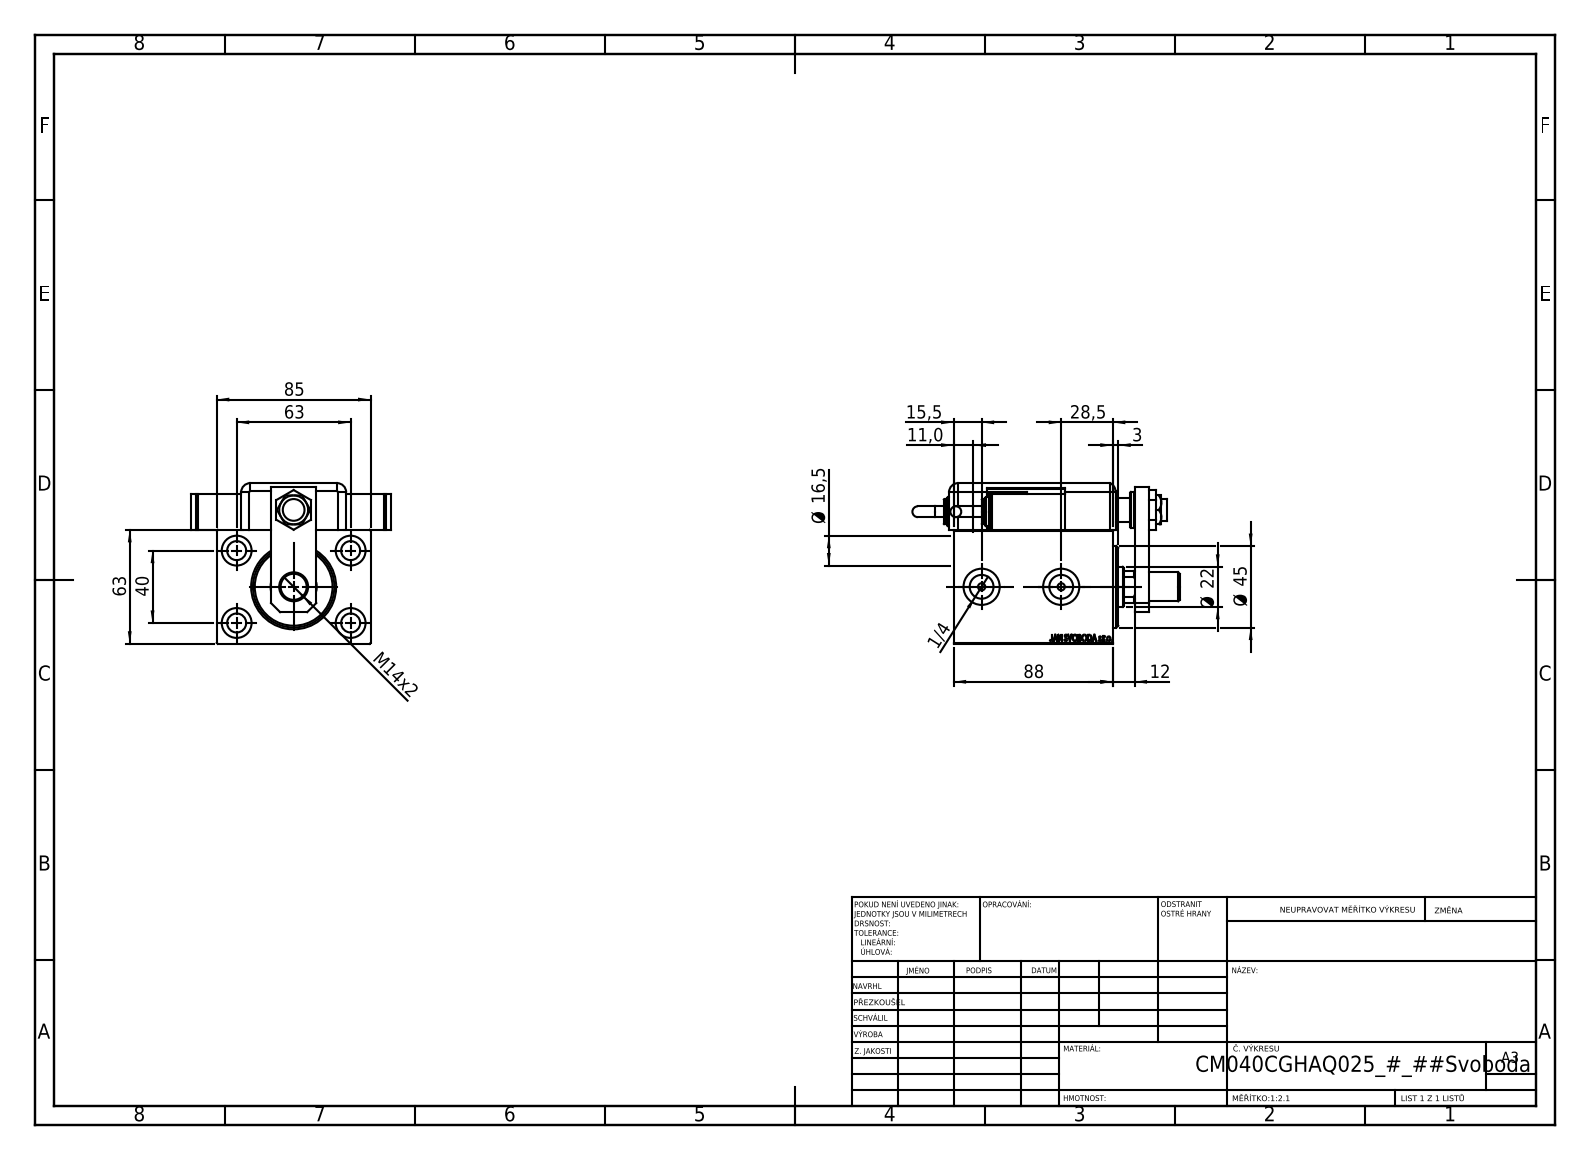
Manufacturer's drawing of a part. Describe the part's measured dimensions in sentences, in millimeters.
The part is named "NUT_D13; NUT_D19; ZARAZKA_Q; SWITCH DIM A_G (+7 more)". Its 3-D file was written by "SolidWorks 2019 (CONFIG_CONTROL_DESIGN)". It is 14 solids with 1260 faces: 618 planar, 119 cylindrical and 523 other. Overall it measures 147.76 by 111 by 88.8 millimeters. Its volume is 547 282 cubic millimeters and its surface area 129 525 square millimeters. Round holes: 4 of diameter 4, 4 of diameter 10.5, 4 of diameter 16.5, 2 of diameter 8, 2 of diameter 13.16, 2 of diameter 14, 2 of diameter 20, 1 of diameter 12, 1 of diameter 12.5, 1 of diameter 13, 1 of diameter 22, 1 of diameter 25.5. Round bosses or shafts: 3 of diameter 20, 3 of diameter 16, 3 of diameter 14, 2 of diameter 6. Partial cylindrical surfaces (rounded edges, fillets, slot ends): 9 of radius 5, 1 of radius 10, 1 of radius 10.5. The main face-to-face distances are 3, 63, 13.5, 12, 85, 83, 10.5, 88, 20, 1.5. The hole center spacings are 37.31, 36.79, 37.86, 38.71, 40, 63, 69.99, 74.63.
